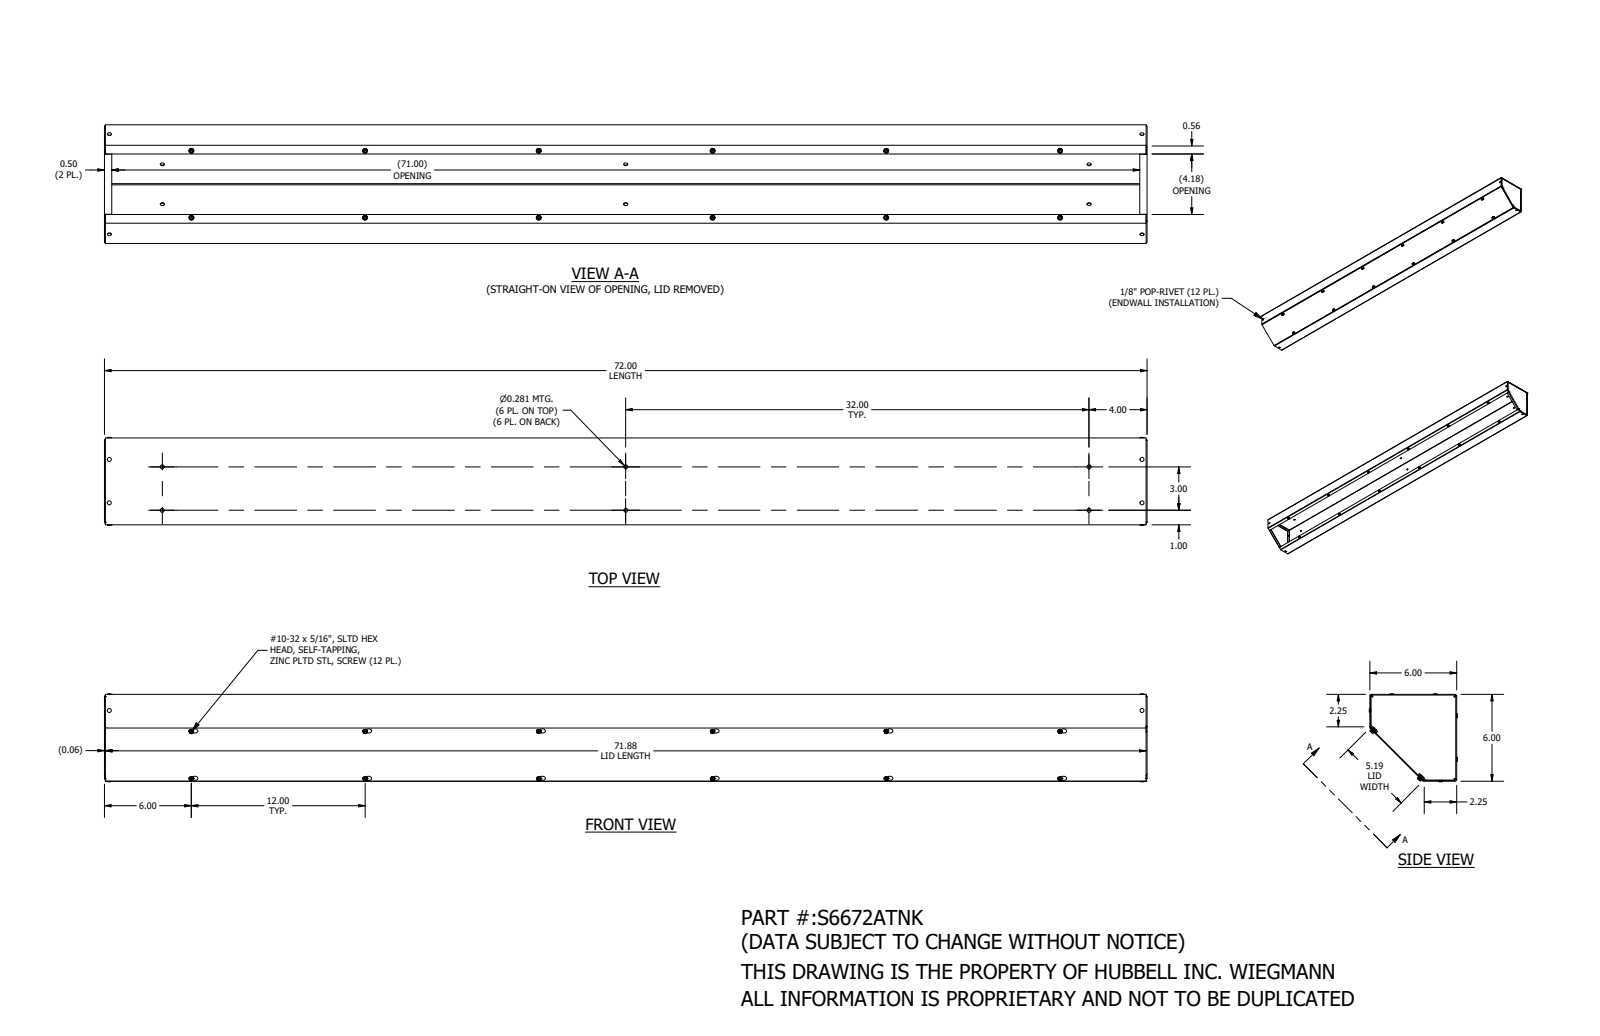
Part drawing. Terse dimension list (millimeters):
name: S6672ATNK
written by: SolidWorks 2021 (AUTOMOTIVE_DESIGN)
unit: mm
bodies: 28 solids, 1314 faces (464 planar, 282 cylindrical, 568 other)
size: 1828.8 × 154.4 × 154.4
volume: 1 521 000 mm³; area: 2 195 000 mm²
holes: 12× ⌀3.3, 12× ⌀4.3, 12× ⌀7.1, 12× ⌀10.3
bosses: 12× ⌀8, 12× ⌀6.7, 12× ⌀4.6, 12× ⌀3.2
rounds: 24× R1.6, 12× R2.8, 10× R1.6, 9× R3, 6× R3, 5× R1.6
face distances: 1.4, 151, 152.4, 149.6, 1.2, 2.6, 1.4, 1827.4, 1828.8, 1826
hole spacings: 304.8, 609.6, 620.8, 6.4, 914.4, 76.2, 298.5, 311.2
